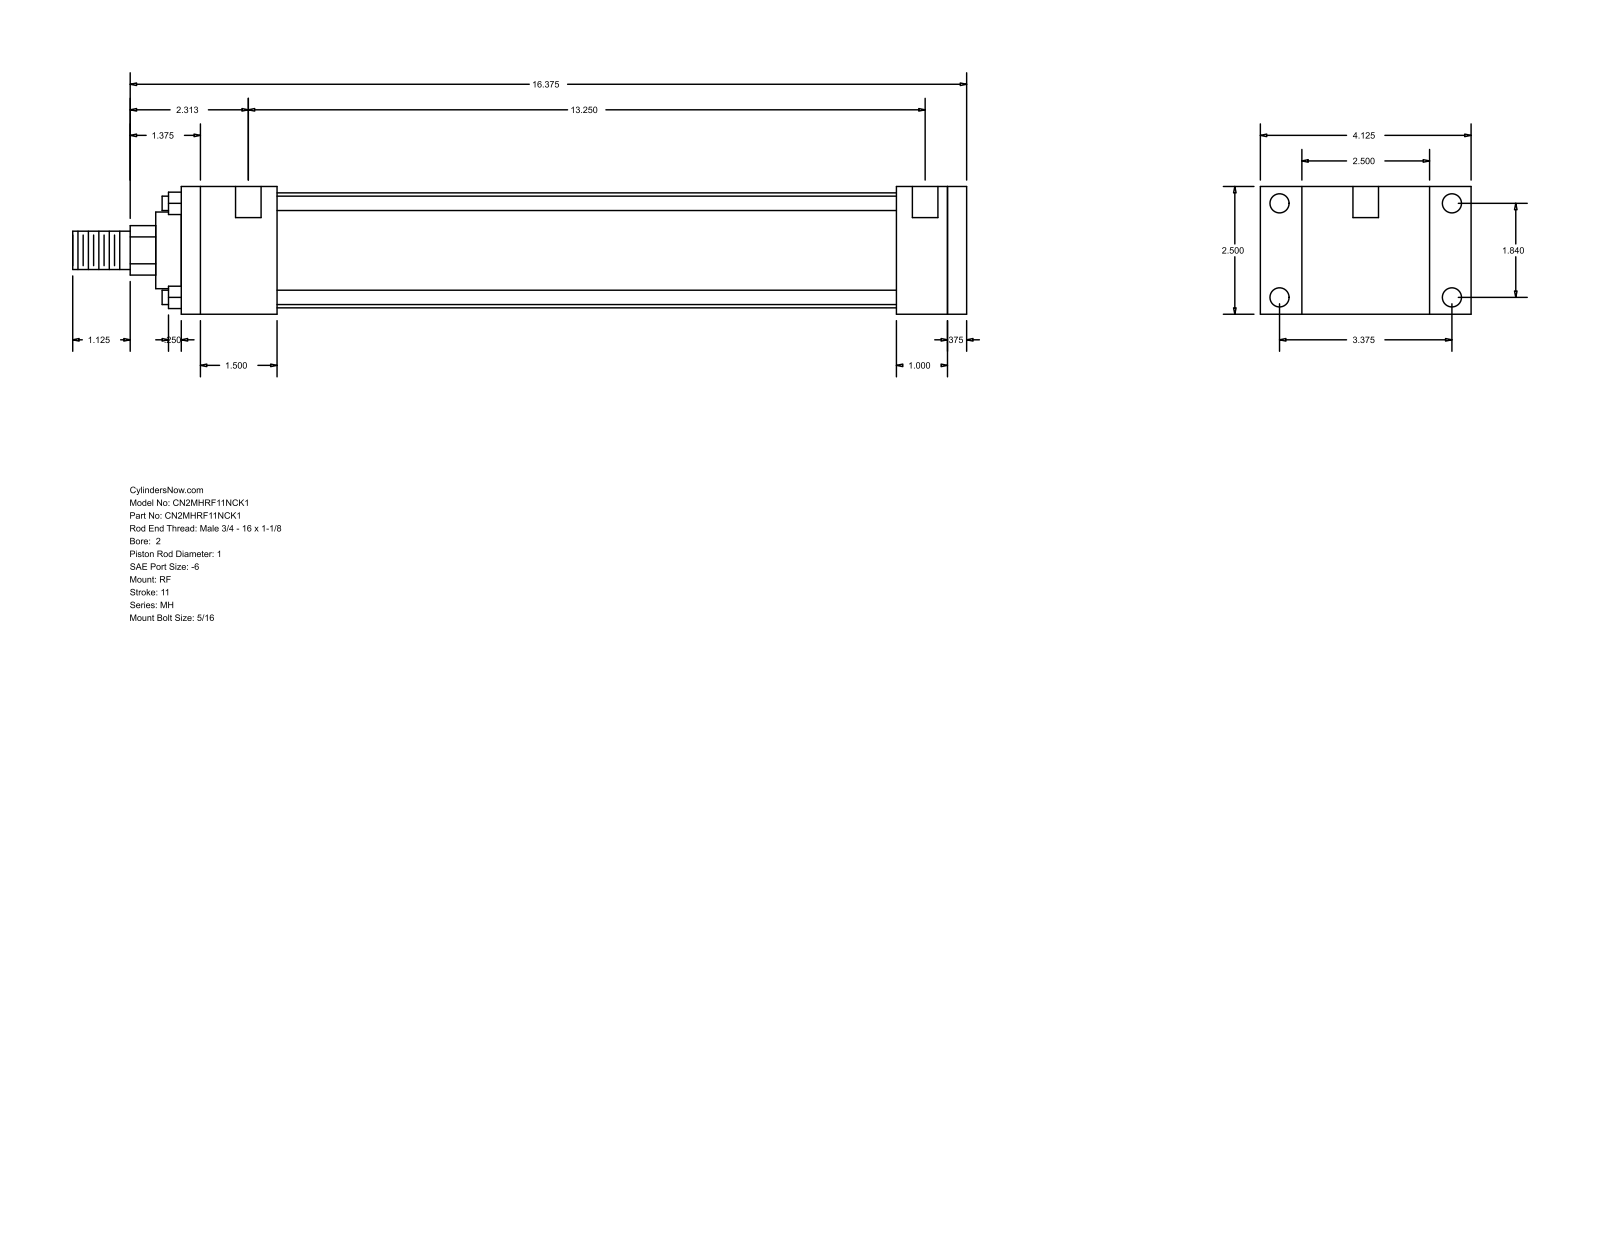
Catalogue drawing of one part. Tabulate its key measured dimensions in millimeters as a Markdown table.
| quantity | value |
| --- | --- |
| part name | MH_RF__0200_1 |
| STEP written by | GSSL Pune (CONFIG_CONTROL_DESIGN) |
| units | millimeters |
| bodies | 0 solids, 92 faces (64 planar, 28 cylindrical, 0 other) |
| overall size | 444.5 × 104.78 × 63.5 |
| round holes (diameter × count) | 5.56 × 4, 9.53 × 4, 12.7 × 2 |
| round bosses / shafts (diameter × count) | 7.14 × 4, 57.15 × 1, 38.1 × 1, 25.4 × 1, 19.05 × 1 |
| partial cylindrical surfaces (radius × count) | 12.29 × 1 |
| main face-to-face distances | 63.5, 390.53, 381, 9.53, 20.64, 25.4, 47.63, 355.6, 307.97, 333.37 |
| hole center spacings | 46.74, 85.72, 97.63, 344.48, 3.17, 4.76, 336.55, 339.72 |
